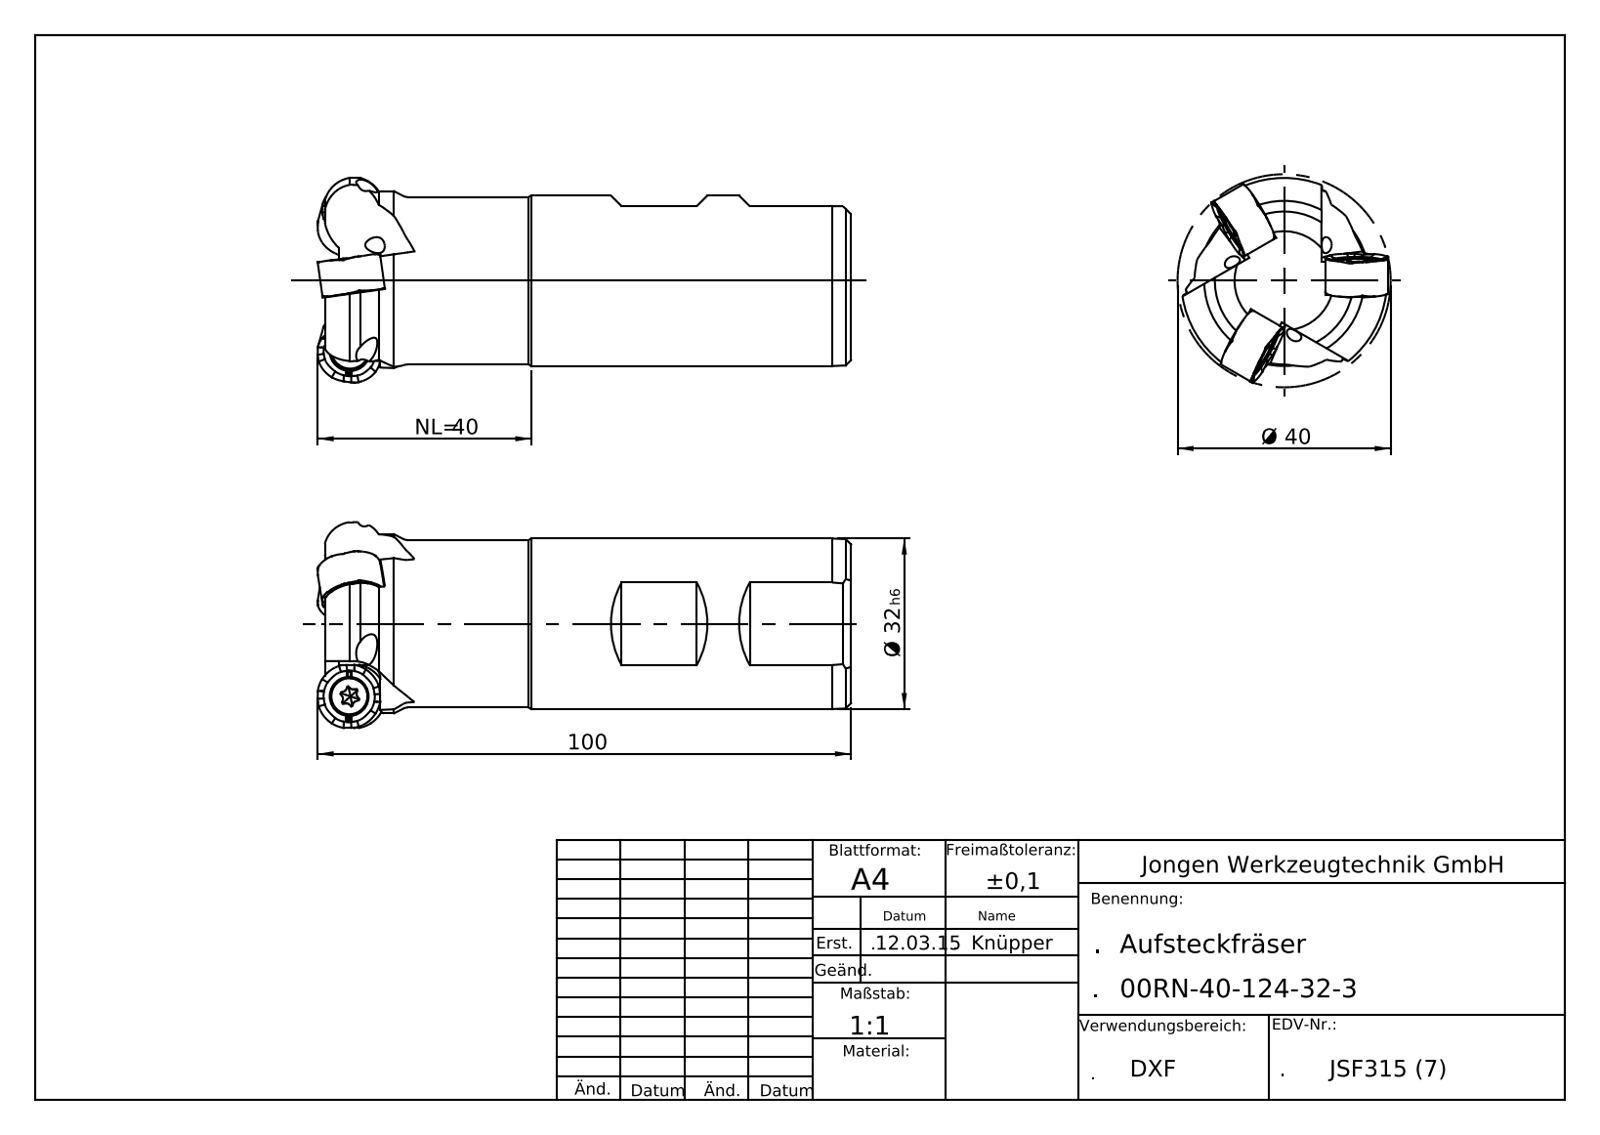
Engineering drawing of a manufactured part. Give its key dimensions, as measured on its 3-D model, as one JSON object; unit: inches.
{"part_name": "00RN_40_124_32_3", "step_written_by": "SolidWorks 2016 (AUTOMOTIVE_DESIGN)", "units": "inches", "bodies": {"solids": 1, "faces": 98, "planar": 35, "cylindrical": 36, "other": 27}, "overall_size": [3.937, 1.573, 1.573], "volume_in3": 4.761, "surface_area_in2": 23.48, "round_holes": [[0.118, 3], [0.256, 1]], "round_bosses_or_shafts": [[1.26, 1], [1.236, 1]], "partial_cylinders_radius": [[0.085, 3], [0.098, 3], [0.177, 3], [0.236, 3], [0.661, 1]], "face_to_face_distances": [3.781, 0.244, 1.156, 0.487, 0.669, 0.024, 0.22, 0.028]}
